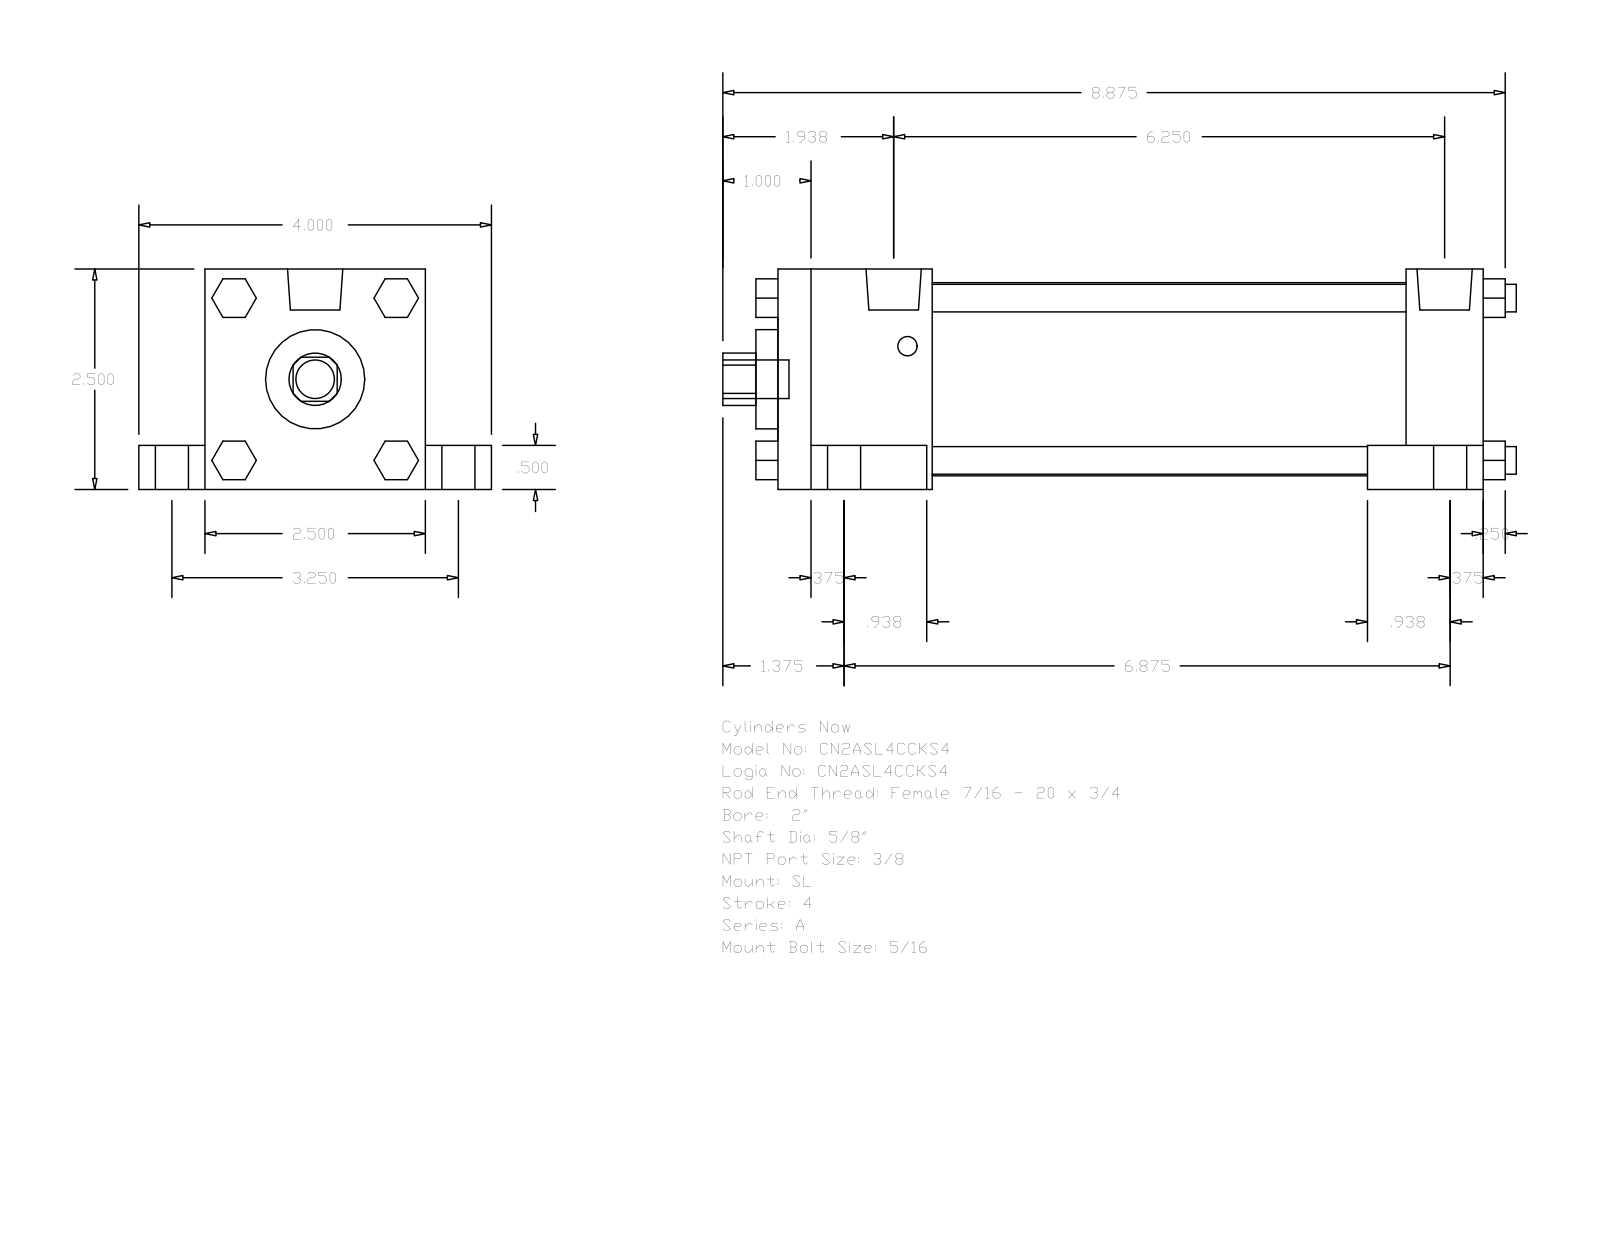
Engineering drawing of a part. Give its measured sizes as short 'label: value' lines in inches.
name: A_SL__0200_0.625
written by: GSSL Pune (CONFIG_CONTROL_DESIGN)
unit: in
bodies: 0 solids, 148 faces (112 planar, 36 cylindrical, 0 other)
size: 9 × 4 × 2.5
holes: 1× ⌀0.625, 1× ⌀1.125, 1× ⌀2.19
bosses: 4× ⌀0.625, 4× ⌀0.375, 4× ⌀0.313, 4× ⌀0.219, 2× ⌀0.627, 1× ⌀0.437
rounds: 1× R0.297
face distances: 2.5, 8, 2, 0.5, 0.75, 3.25, 1.75, 6.25, 7.125, 5.375
